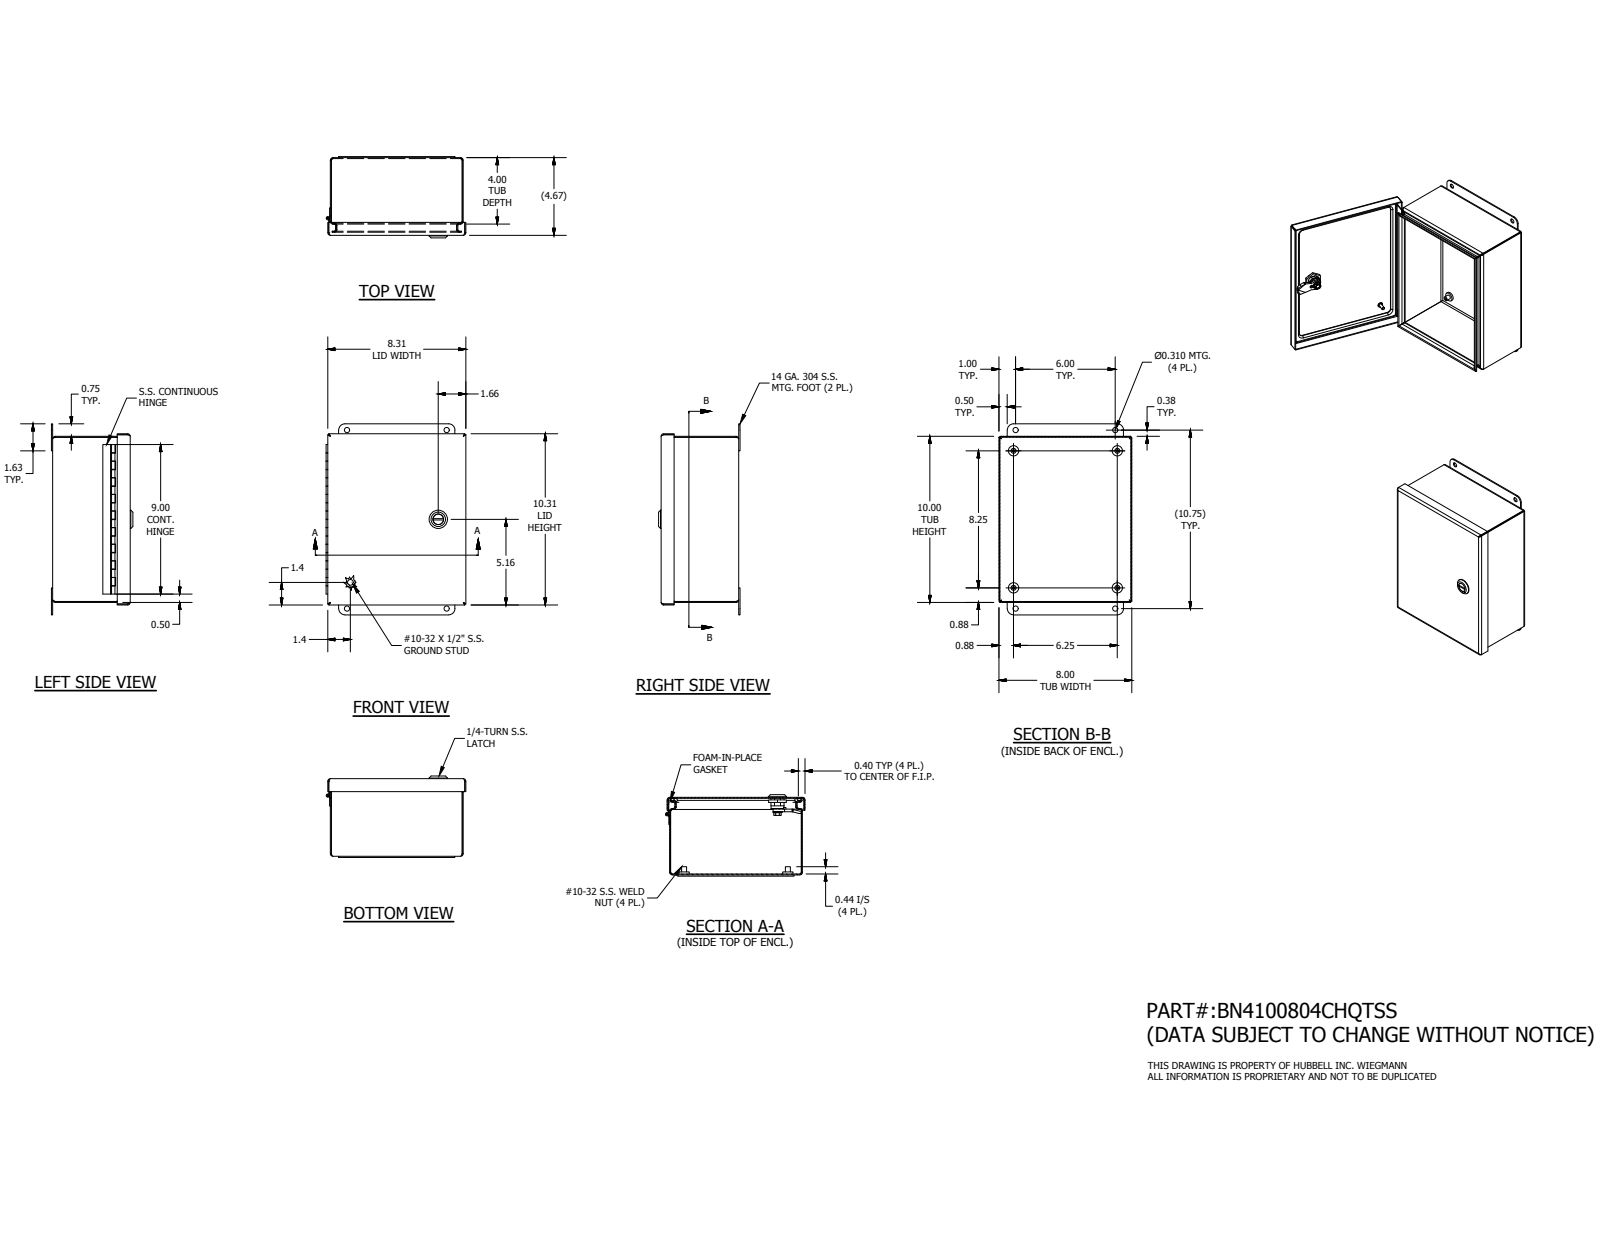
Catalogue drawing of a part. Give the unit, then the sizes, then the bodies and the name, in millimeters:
Units: millimetres
Overall size (bounding box): 292.1 × 213.66 × 124.59
Round holes (diameter × count): ⌀3.96 ×4, ⌀7.87 ×4, ⌀2.96 ×1, ⌀5 ×1, ⌀8 ×1, ⌀10 ×1, ⌀10.2 ×1, ⌀16.1 ×1
Round bosses / shafts (diameter × count): ⌀15.88 ×4, ⌀7.62 ×4, ⌀28 ×1, ⌀19.8 ×1, ⌀16 ×1, ⌀15.2 ×1, ⌀13.5 ×1, ⌀12.8 ×1
Partial cylindrical surfaces — rounded edges, fillets, slot ends (radius × count): R2.38 ×20, R3.88 ×20, R3.17 ×16, R0.5 ×8, R4 ×4, R9.53 ×4, R2.31 ×2, R6.45 ×1
Main face-to-face distances: 1.5, 1.49, 117.19, 118.68, 115.69, 117.18, 252.5, 200.21, 201.7, 201.71
Hole centre spacings: 31.91, 241.32, 152.4, 158.75, 158.78, 158.79, 177.17, 209.55
Volume: 450 081 mm³ · Surface area: 555 703 mm²
Bodies: 19 solids, 608 faces (323 planar, 191 cylindrical, 94 other)
Part name (STEP PRODUCT): BN41008CHQTSSLID; 10x8; 34854; H4050549LH (+8 more)
STEP written by: Autodesk Inventor 2016 (AUTOMOTIVE_DESIGN)
